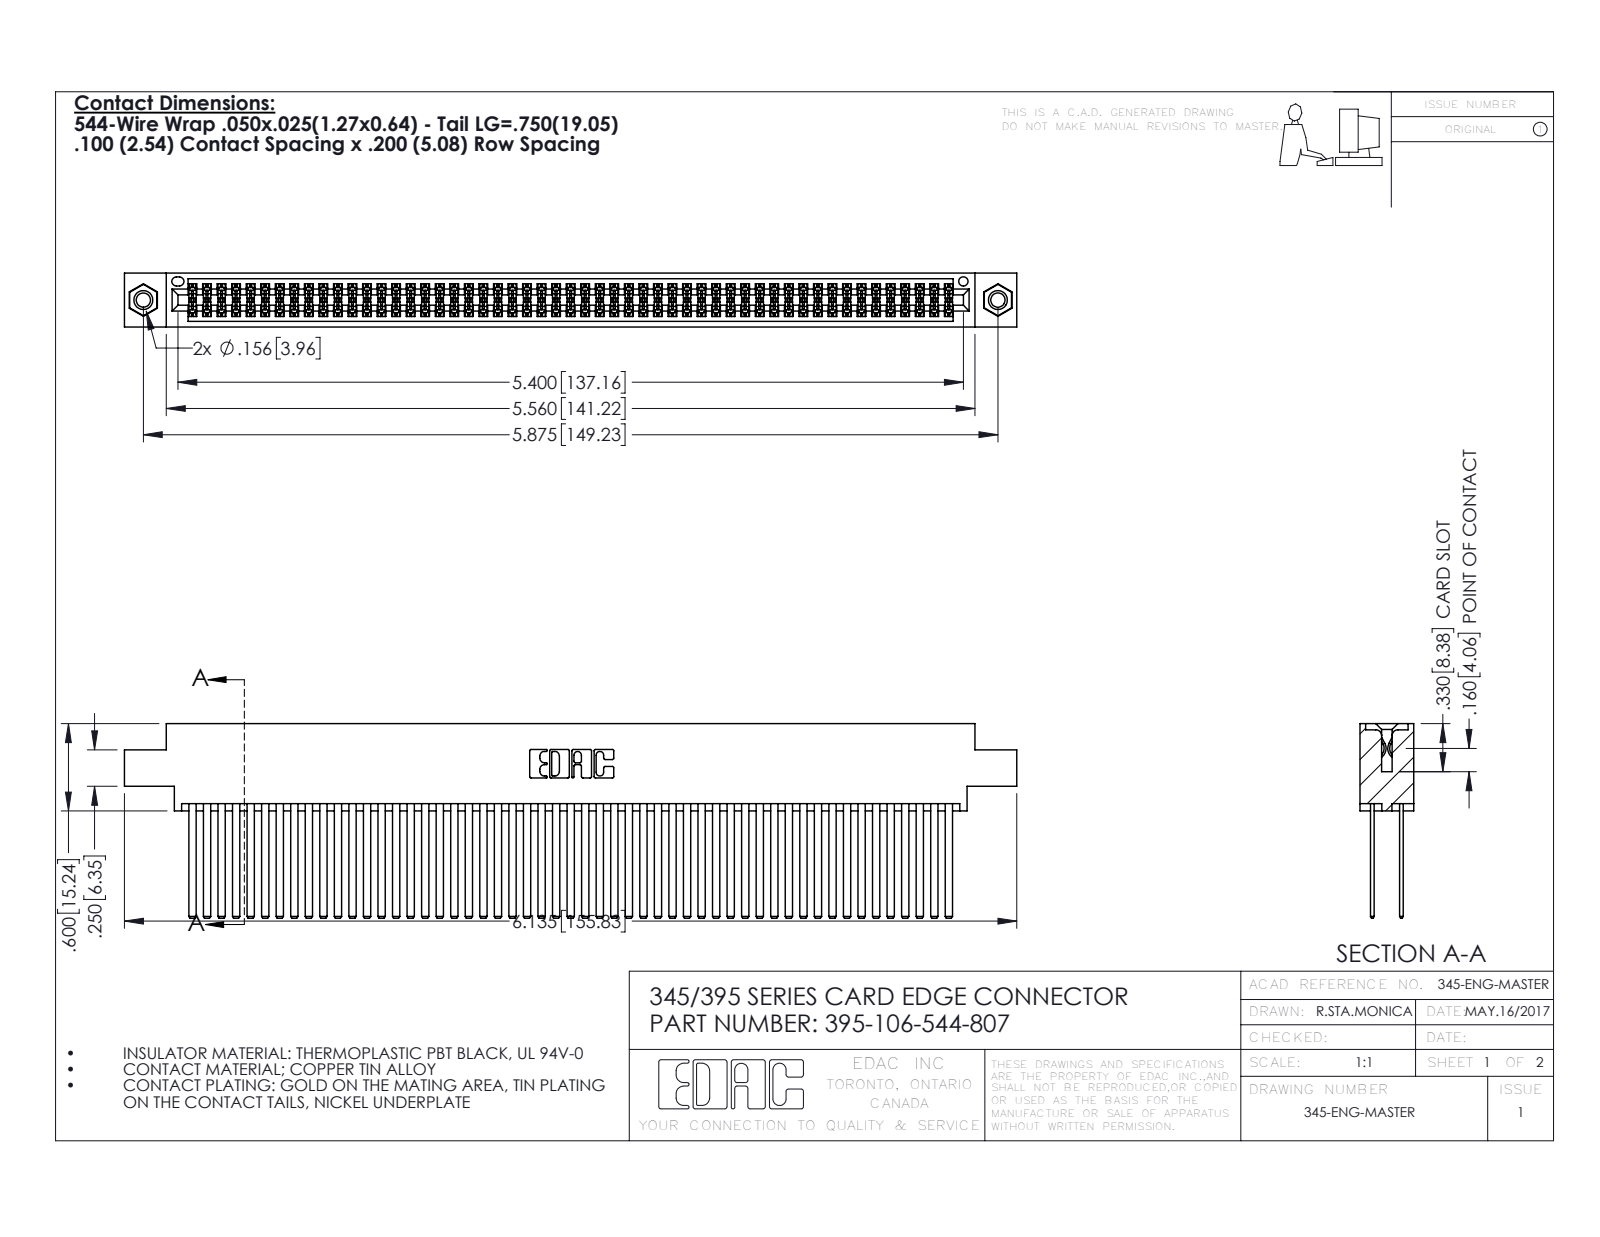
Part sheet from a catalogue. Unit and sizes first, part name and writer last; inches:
Units: inches
Overall size (bounding box): 6.135 × 1.337 × 0.37
Round holes (diameter × count): ⌀0.098 ×2, ⌀0.125 ×2, ⌀0.156 ×2, ⌀0.064 ×1
Round bosses / shafts (diameter × count): ⌀0.155 ×2
Partial cylindrical surfaces — rounded edges, fillets, slot ends (radius × count): R0.006 ×159, R0.01 ×22, R0.007 ×6, R0.031 ×6, R0.026 ×3, R0.014 ×2, R0.019 ×2, R0.022 ×2
Main face-to-face distances: 0.2, 0.025, 0.072, 0.098, 0.272, 0.298, 0.225, 0.175, 0.37, 0.15
Hole centre spacings: 0.27, 5.639, 5.875
Volume: 1.013 in³ · Surface area: 45.38 in²
Bodies: 109 solids, 4854 faces (3190 planar, 1648 cylindrical, 16 other)
Part name (STEP PRODUCT): 345-292-001_345-293-144; 345-250-001_345-250-005-103; 395-106-544-807; 345 Part_0.170 Offset - 0.156 Dia-TI
STEP written by: SolidWorks 2016 (CONFIG_CONTROL_DESIGN)
